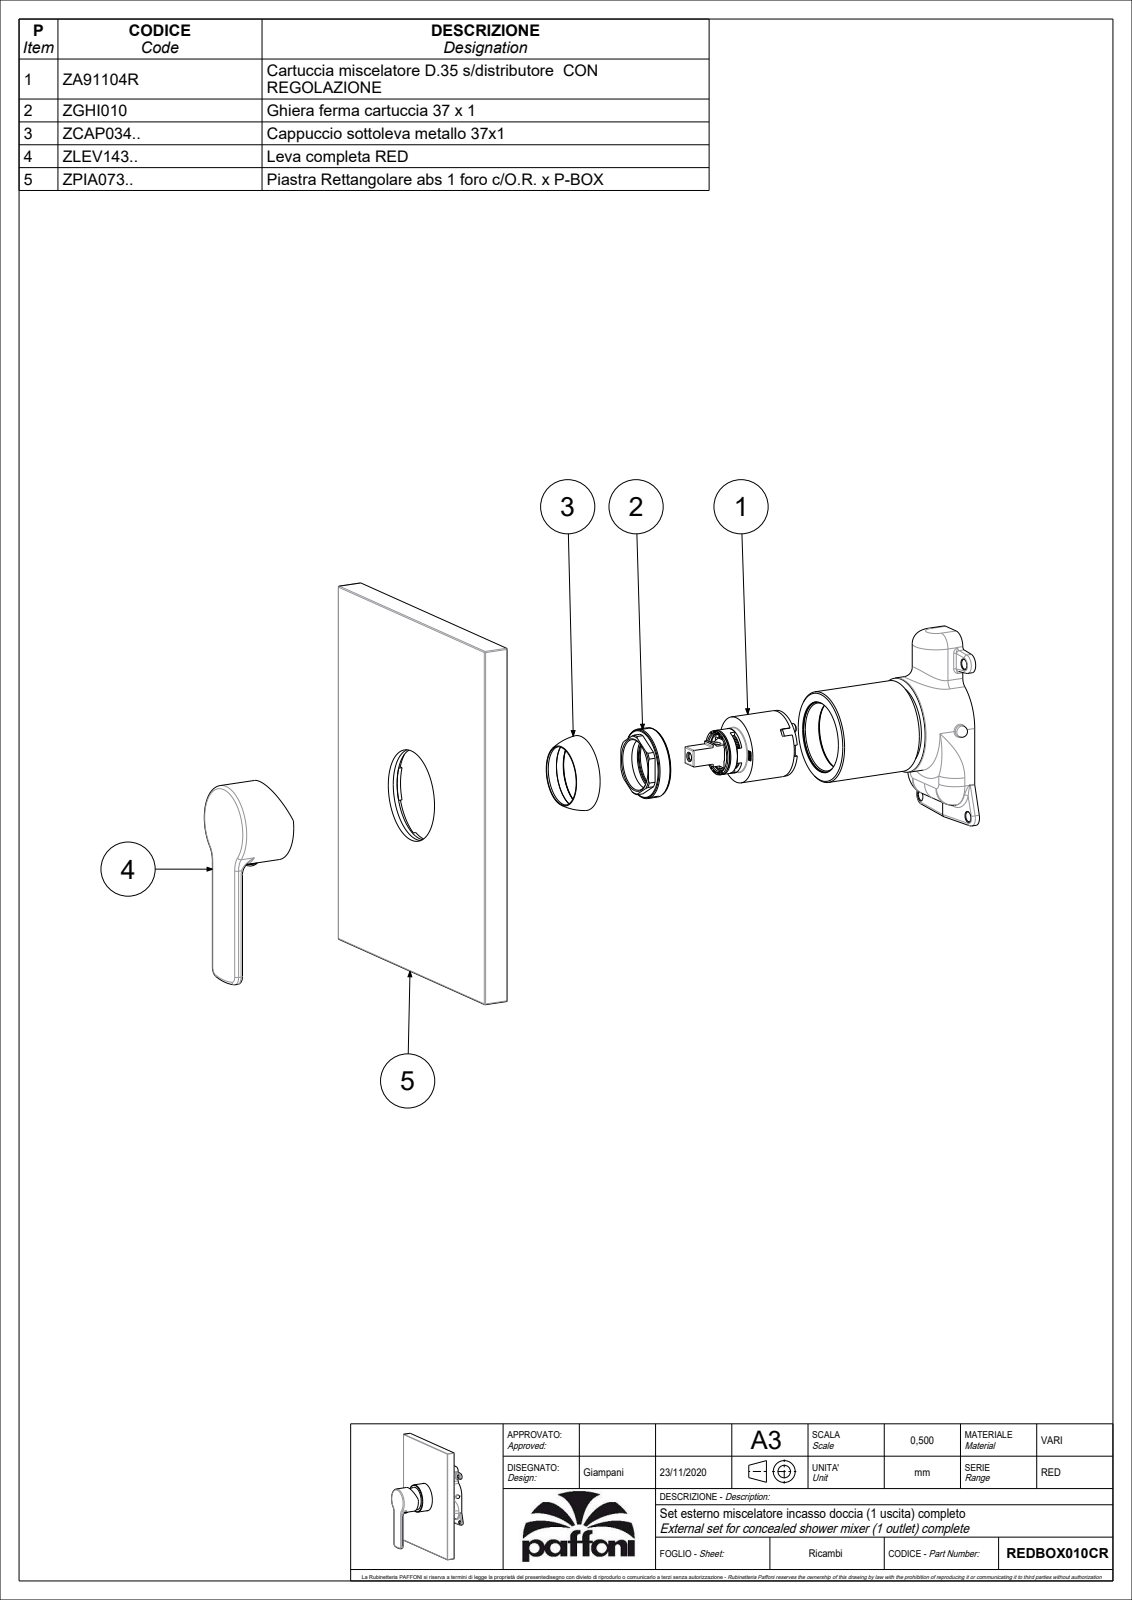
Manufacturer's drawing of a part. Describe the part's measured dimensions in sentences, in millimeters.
The part is named "REDBOX010CR". Its 3-D file was written by "CREO PARAMETRIC BY PTC INC, 2020044 (CONFIG_CONTROL_DESIGN)". It is 2 solids with 1139 faces: 638 planar, 297 cylindrical and 204 other. Overall it measures 192 by 154 by 70.33 millimeters. Its volume is 300 615 cubic millimeters and its surface area 119 954 square millimeters. Round holes: 3 of diameter 5, 3 of diameter 7, 2 of diameter 2, 2 of diameter 3.3, 2 of diameter 4, 1 of diameter 3, 1 of diameter 4.5, 1 of diameter 19.5, 1 of diameter 19.9, 1 of diameter 26.8, 1 of diameter 29, 1 of diameter 31. Round bosses or shafts: 2 of diameter 4.8, 1 of diameter 57, 1 of diameter 48.1, 1 of diameter 43, 1 of diameter 39, 1 of diameter 35, 1 of diameter 34.8, 1 of diameter 32.2. Partial cylindrical surfaces (rounded edges, fillets, slot ends): 74 of radius 0.5, 11 of radius 0.15, 4 of radius 0.3, 4 of radius 1.5, 2 of radius 1, 2 of radius 5, 2 of radius 10, 1 of radius 2.5. The main face-to-face distances are 13.5, 3, 10.5, 23.5, 130.5, 154, 20, 168.5, 192, 65.6. The hole center spacings are 8.6, 13.45, 15.13, 21.93, 12.5, 14, 18.
